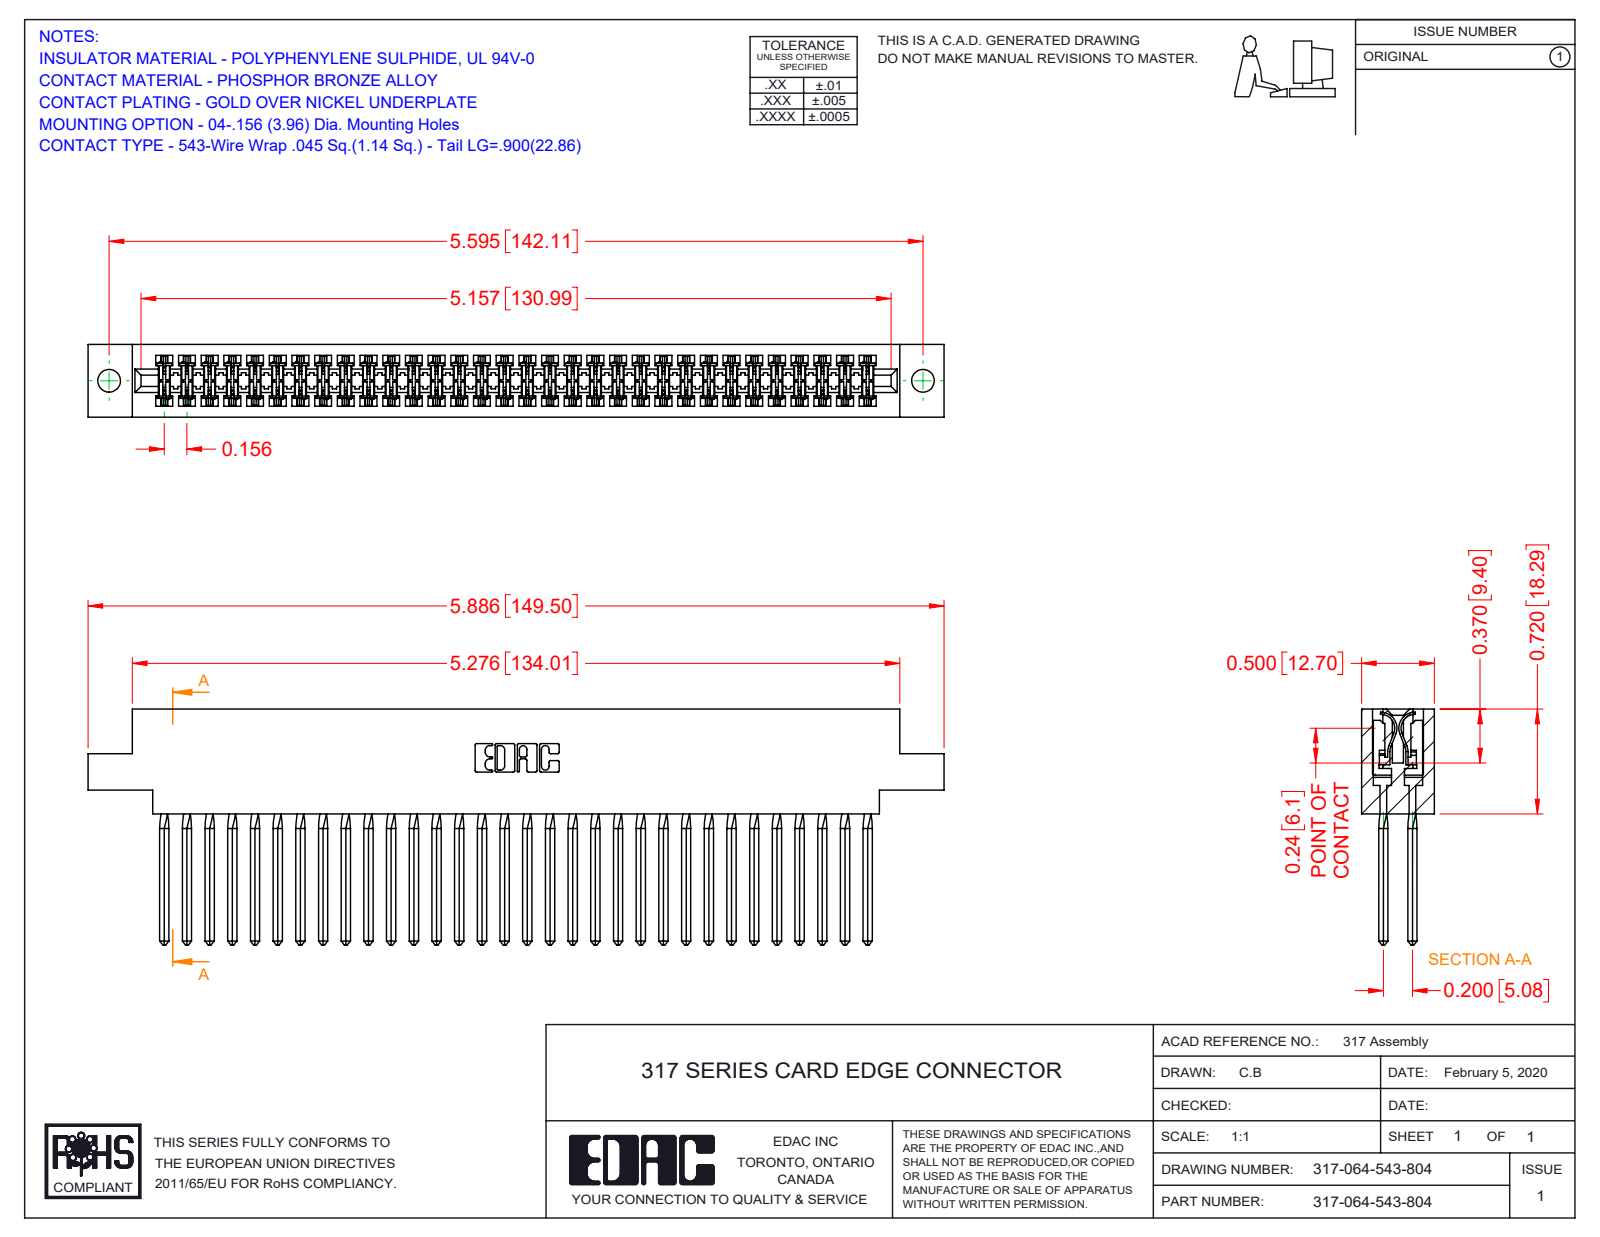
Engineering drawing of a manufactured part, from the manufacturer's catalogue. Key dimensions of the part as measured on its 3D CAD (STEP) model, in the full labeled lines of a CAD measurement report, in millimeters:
Part name (STEP PRODUCT): 317-064-543-804; 317-290-001_543; 317 Part_.156 Dia - TH
STEP written by: SolidWorks 2016 (CONFIG_CONTROL_DESIGN)
Units: millimetres
Bodies: 65 solids, 5798 faces (4730 planar, 812 cylindrical, 256 other)
Overall size (bounding box): 149.5 × 41.1 × 12.7
Volume: 24 990 mm³ · Surface area: 37 340 mm²
Round holes (diameter × count): ⌀4 ×2
Partial cylindrical surfaces — rounded edges, fillets, slot ends (radius × count): R0.4 ×128, R0.3 ×22, R0.2 ×6, R0.8 ×6, R0.7 ×3, R2.4 ×2, R2.5 ×2, R2.8 ×2
Main face-to-face distances: 12.7, 1.9, 10.8, 8.9, 2.8, 5, 2.4, 5.1, 2.9, 3.3
Hole centre spacings: 142.1
